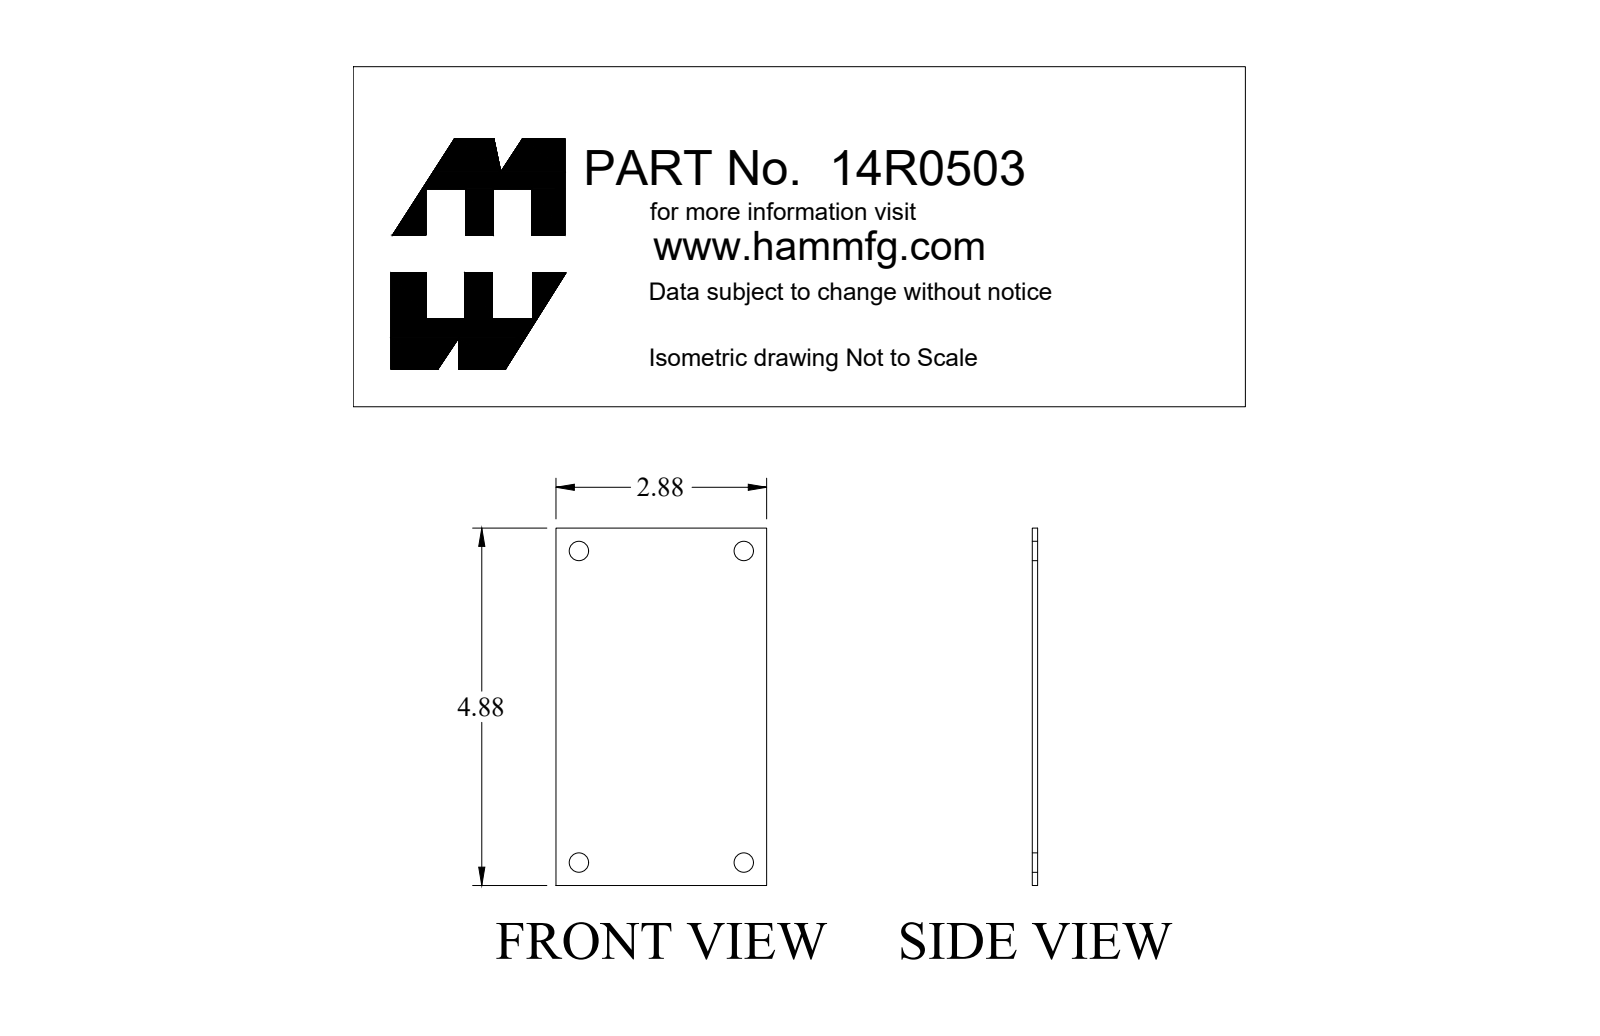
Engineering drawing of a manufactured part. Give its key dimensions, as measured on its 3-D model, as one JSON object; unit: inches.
{"part_name": "14R0503", "step_written_by": "SolidWorks 2018 (AUTOMOTIVE_DESIGN)", "units": "inches", "bodies": {"solids": 1, "faces": 10, "planar": 6, "cylindrical": 4, "other": 0}, "overall_size": [4.875, 2.875, 0.072], "volume_in3": 0.993, "surface_area_in2": 28.95, "round_holes": [[0.265, 4]], "face_to_face_distances": [0.072, 2.875, 4.875], "hole_center_spacings": [2.25, 4.25, 4.808]}
